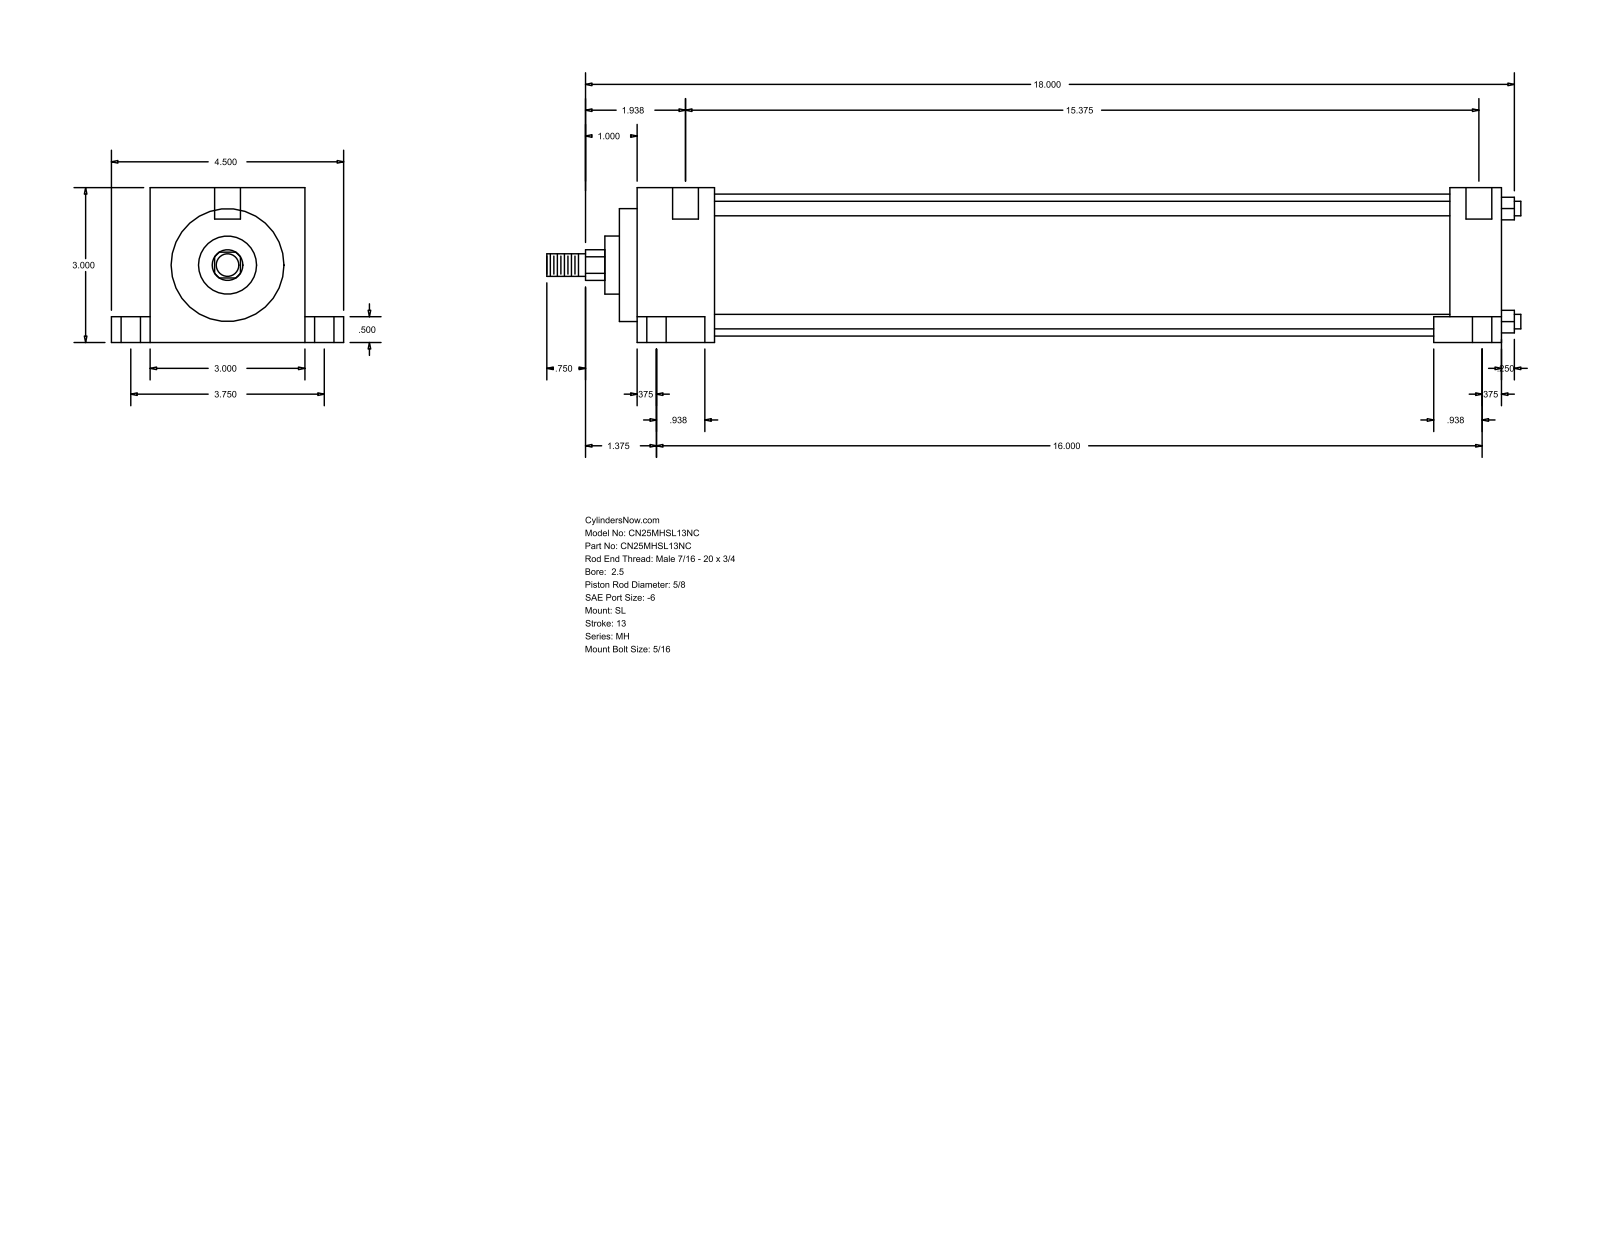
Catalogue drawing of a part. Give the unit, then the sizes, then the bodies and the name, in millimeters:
Units: millimetres
Overall size (bounding box): 479.43 × 114.3 × 76.2
Round holes (diameter × count): ⌀5.56 ×2, ⌀9.53 ×2, ⌀15.88 ×2, ⌀12.7 ×1
Round bosses / shafts (diameter × count): ⌀7.14 ×4, ⌀69.85 ×1, ⌀55.55 ×1, ⌀28.57 ×1, ⌀15.88 ×1, ⌀11.11 ×1
Partial cylindrical surfaces — rounded edges, fillets, slot ends (radius × count): R7.54 ×1
Main face-to-face distances: 76.2, 25.4, 408.78, 434.18, 63.5, 12.7, 19.05, 95.25, 31.75, 400.84
Hole centre spacings: 47.65, 3.17, 95.24
Bodies: 0 solids, 86 faces (61 planar, 25 cylindrical, 0 other)
Part name (STEP PRODUCT): MH_SL__0250_0.625
STEP written by: GSSL Pune (CONFIG_CONTROL_DESIGN)
